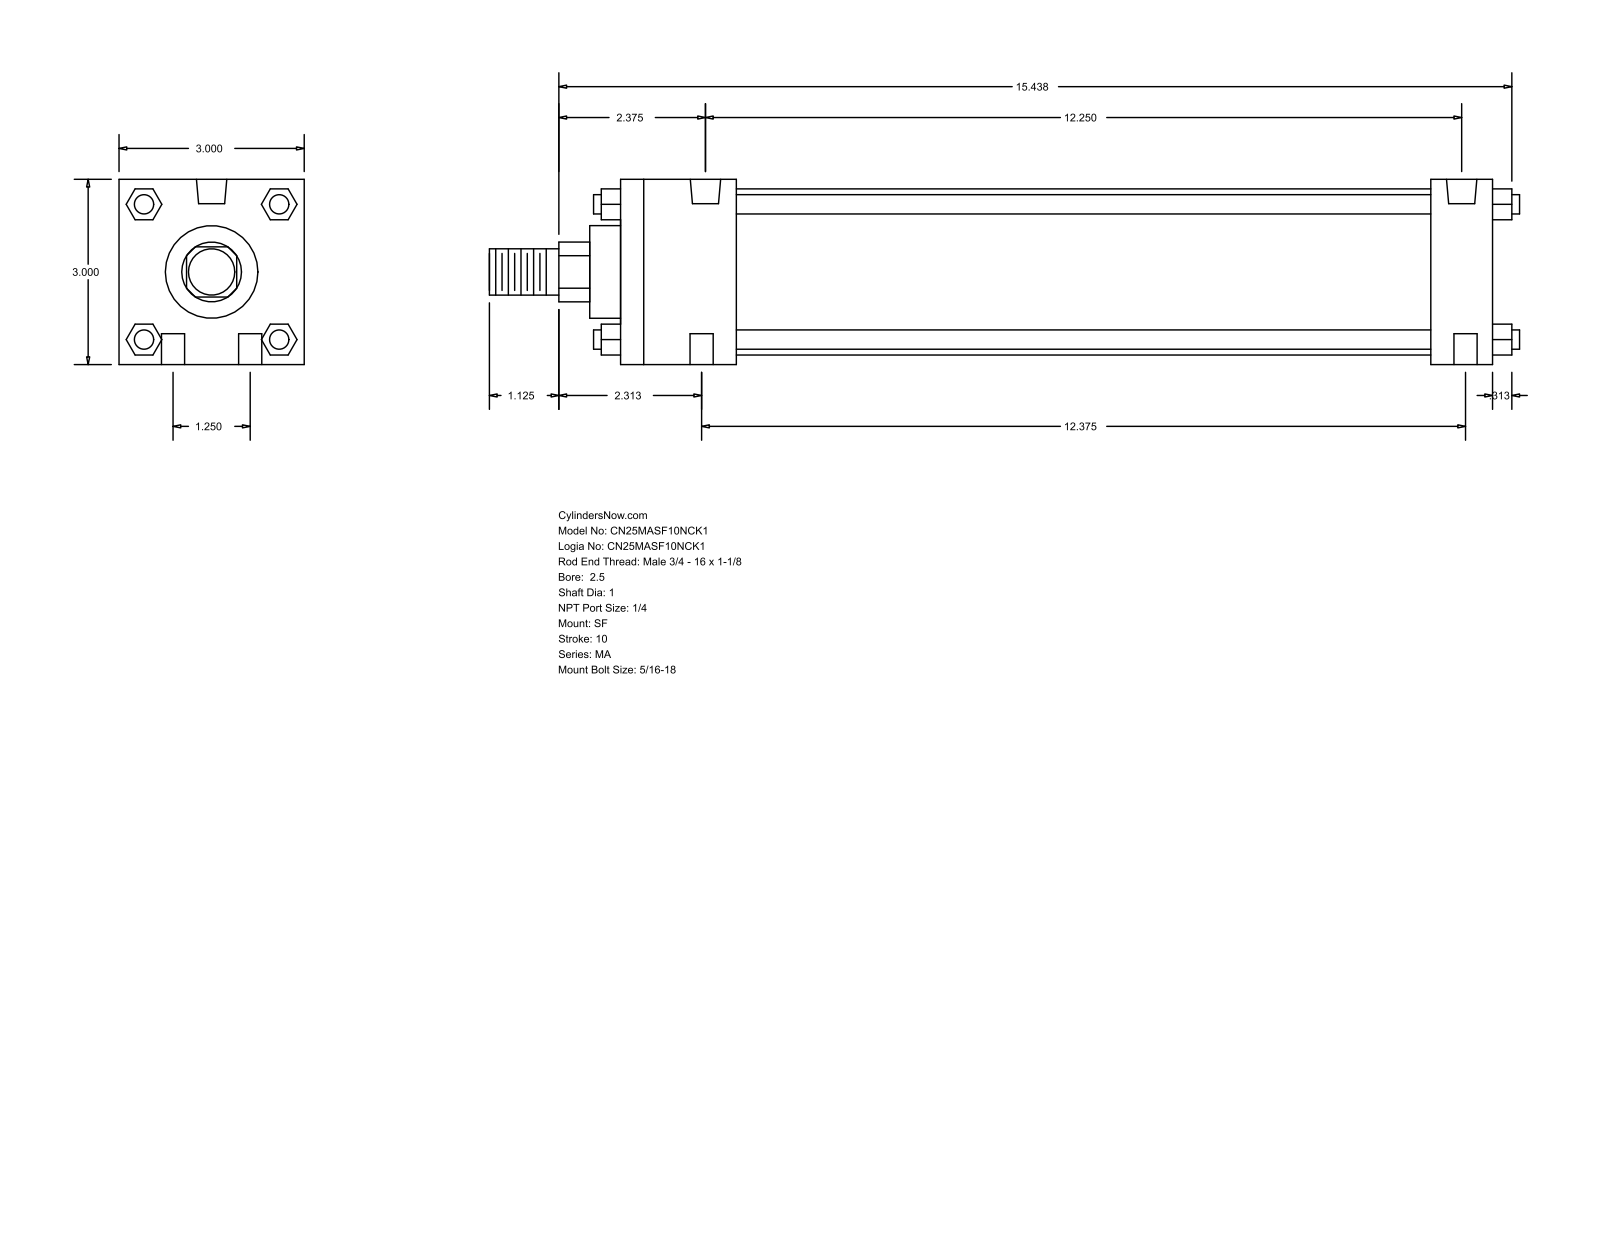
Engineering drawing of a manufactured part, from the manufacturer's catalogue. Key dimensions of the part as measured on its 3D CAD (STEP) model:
Part name (STEP PRODUCT): MA_SF__0250_1
STEP written by: GSSL Pune (CONFIG_CONTROL_DESIGN)
Units: millimetres
Bodies: 0 solids, 124 faces (94 planar, 30 cylindrical, 0 other)
Overall size (bounding box): 423.86 × 76.2 × 76.2
Round holes (diameter × count): ⌀9.53 ×4, ⌀7.94 ×2, ⌀12.49 ×2
Round bosses / shafts (diameter × count): ⌀7.94 ×4, ⌀68.33 ×1, ⌀38.1 ×1, ⌀25.4 ×1, ⌀19.05 ×1
Partial cylindrical surfaces — rounded edges, fillets, slot ends (radius × count): R12.29 ×1
Main face-to-face distances: 76.2, 358.78, 12.7, 333.37, 25.41, 47.63, 285.74, 311.15, 27.81, 48.17
Hole centre spacings: 15.96, 31.76, 311.15, 313.13, 313.14, 314.32, 315.92
